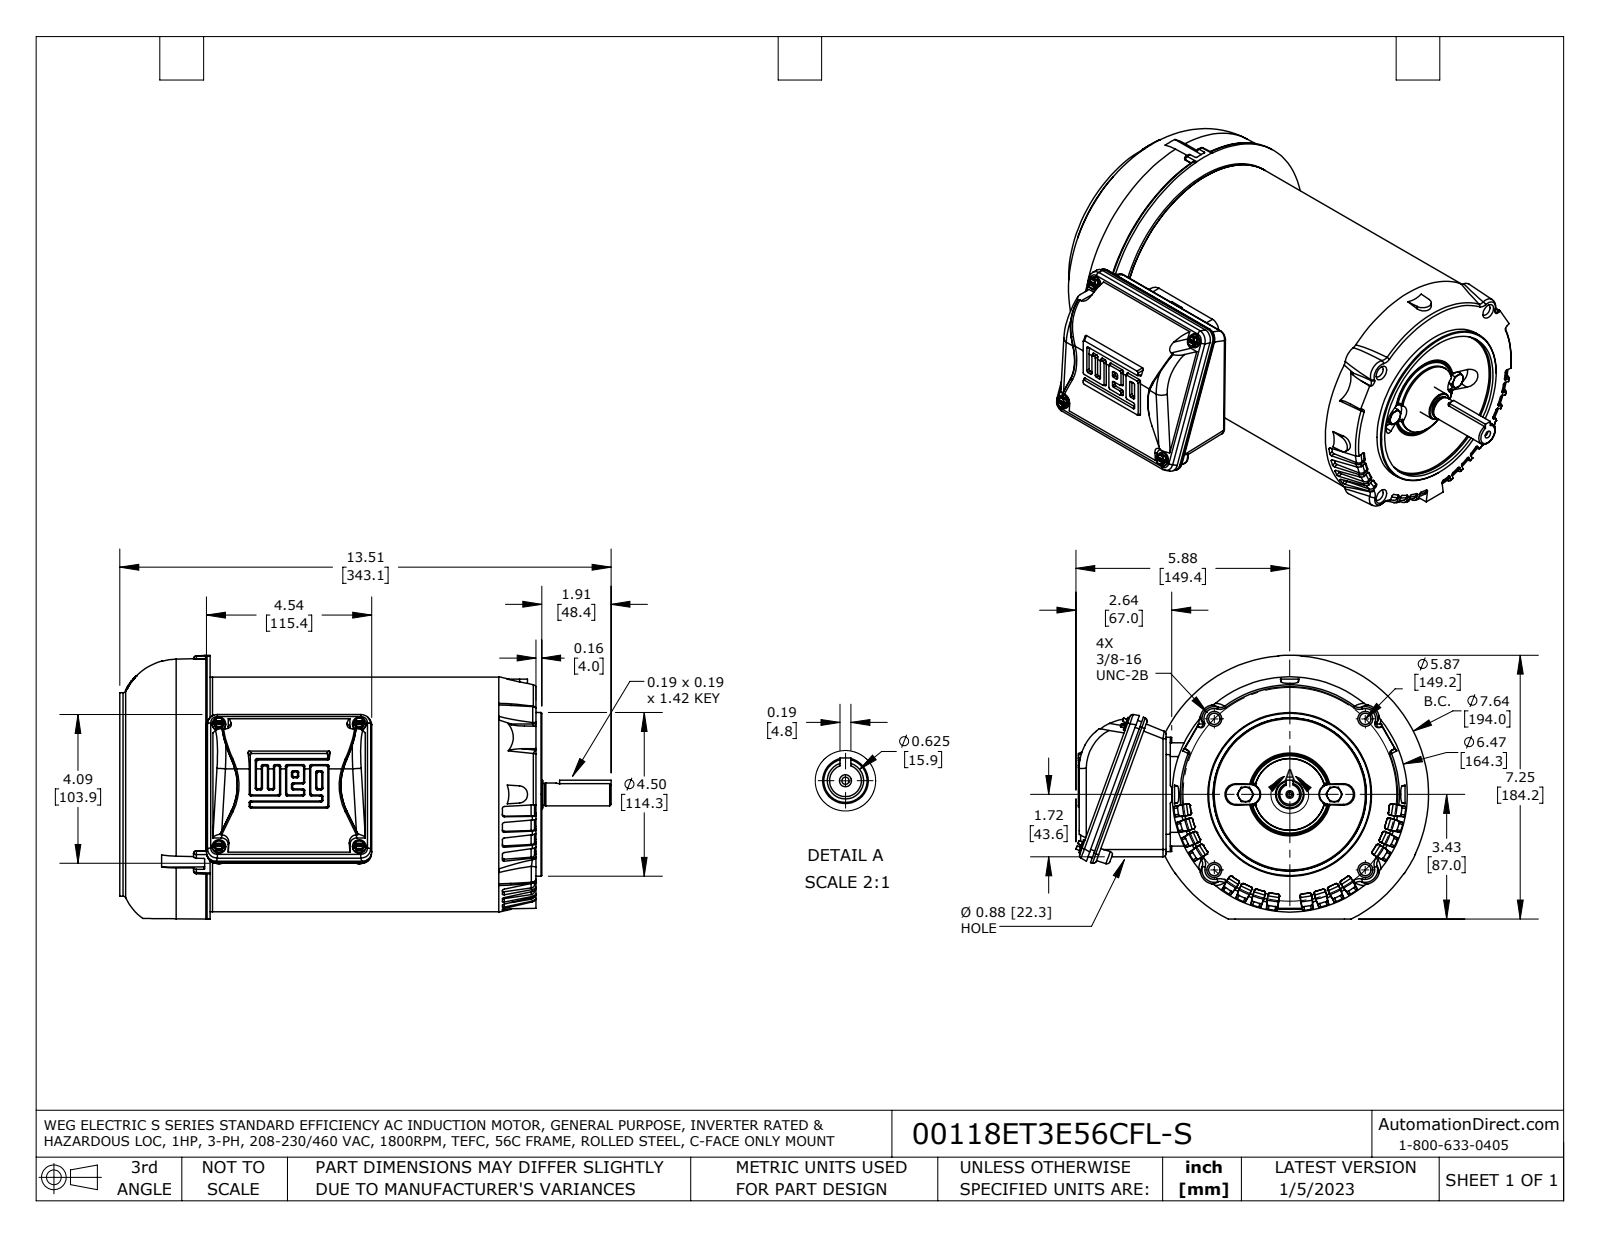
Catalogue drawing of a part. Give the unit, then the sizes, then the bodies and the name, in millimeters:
Units: millimetres
Overall size (bounding box): 343.1 × 246.4 × 191.8
Round holes (diameter × count): ⌀8 ×4, ⌀3.1 ×1
Round bosses / shafts (diameter × count): ⌀9.5 ×4, ⌀8.9 ×2, ⌀163.8 ×1, ⌀163.8 ×1, ⌀142 ×1, ⌀114.3 ×1, ⌀19.9 ×1, ⌀15.9 ×1
Partial cylindrical surfaces — rounded edges, fillets, slot ends (radius × count): R1.2 ×40, R0.2 ×38, R1.3 ×32, R1.5 ×12, R2.2 ×12, R0.5 ×10, R5.2 ×8, R7 ×8
Main face-to-face distances: 201.7, 58, 259.7, 285.7, 227.7, 26, 5, 63, 264.7, 290.7
Hole centre spacings: 74.6, 105.5, 149.2
Volume: 6 887 000 mm³ · Surface area: 363 900 mm²
Bodies: 12 solids, 1274 faces (471 planar, 275 cylindrical, 528 other)
Part name (STEP PRODUCT): 56C_3PH_TEFC_GP_13504_FL fxt
STEP written by: SolidWorks 2021 (AUTOMOTIVE_DESIGN)
